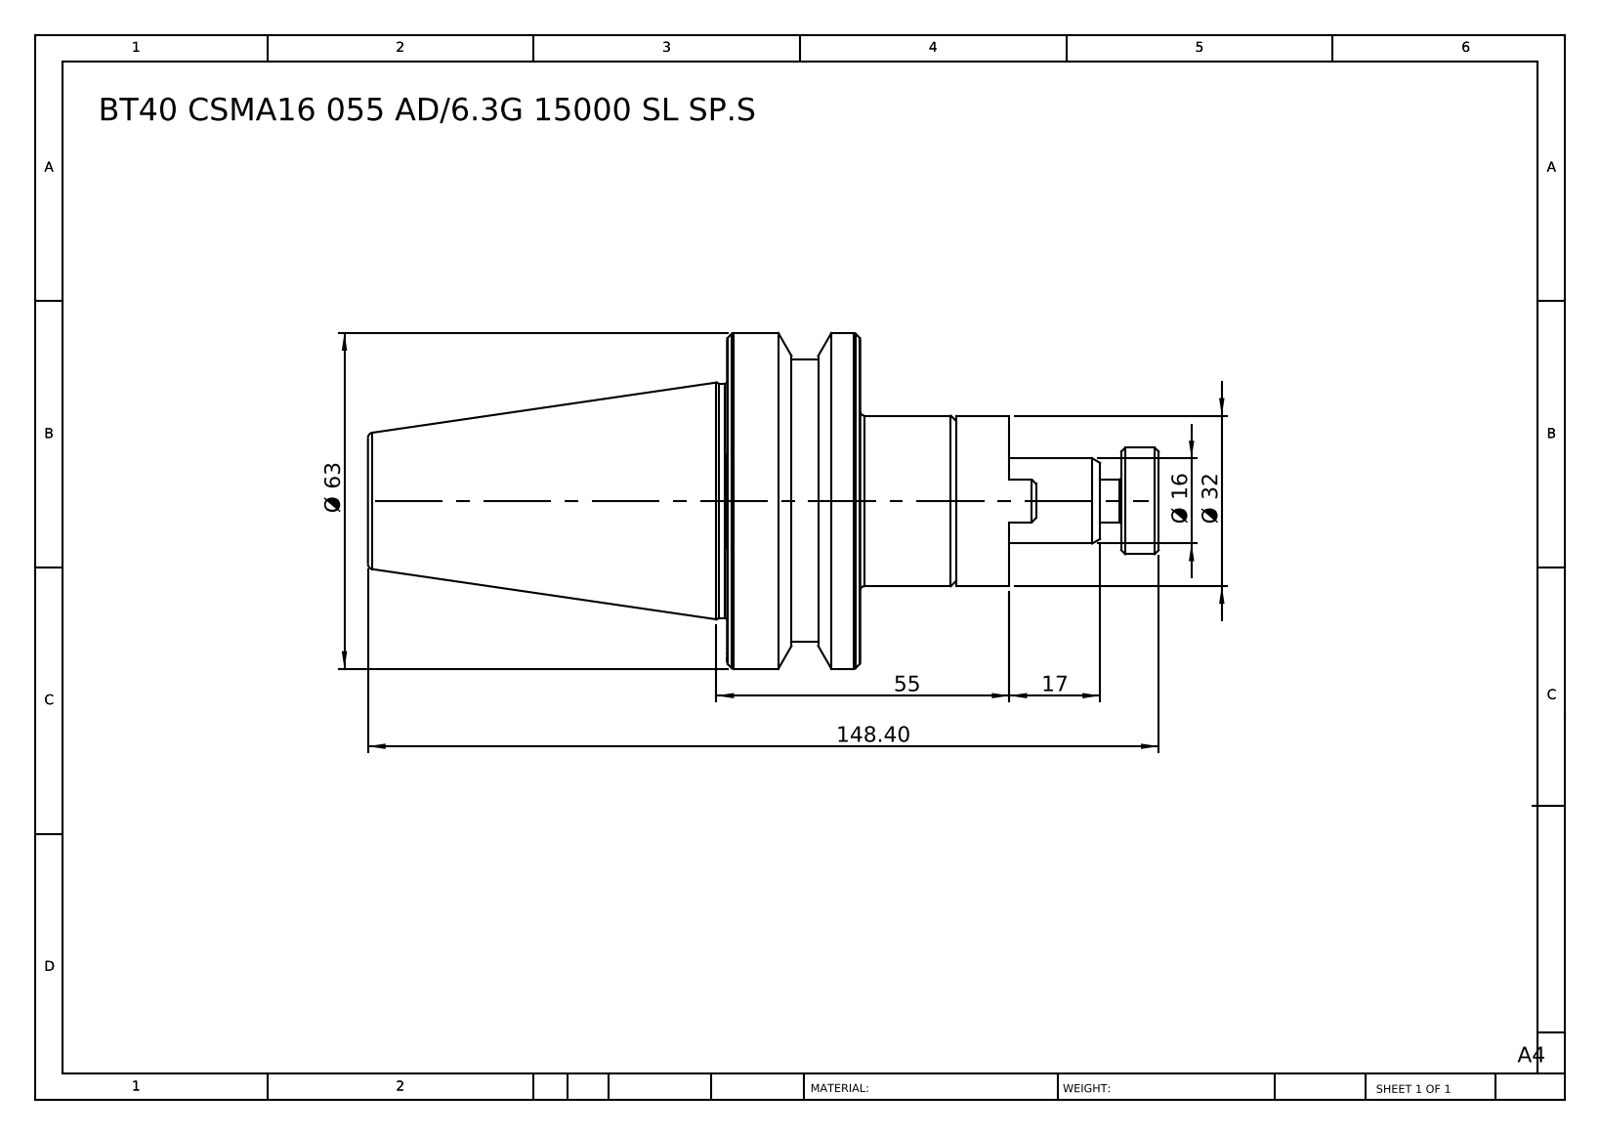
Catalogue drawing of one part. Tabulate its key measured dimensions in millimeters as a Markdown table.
| quantity | value |
| --- | --- |
| part name | BT40 CSMA16 070 AD 6.3G15000 SL SP |
| STEP written by | SolidWorks 2014 (CONFIG_CONTROL_DESIGN) |
| units | millimeters |
| bodies | 2 solids, 94 faces (22 planar, 22 cylindrical, 50 other) |
| overall size | 148.4 × 63 × 63 |
| volume | 167 227 mm³ |
| surface area | 25 409 mm² |
| round holes (diameter × count) | 16 × 1 |
| round bosses / shafts (diameter × count) | 63 × 1, 53 × 1, 44 × 1, 32 × 1, 20 × 1, 15.6 × 1, 8 × 1 |
| main face-to-face distances | 25, 18, 43, 28, 10, 53, 120.4, 110.4, 92.4, 67.4 |
